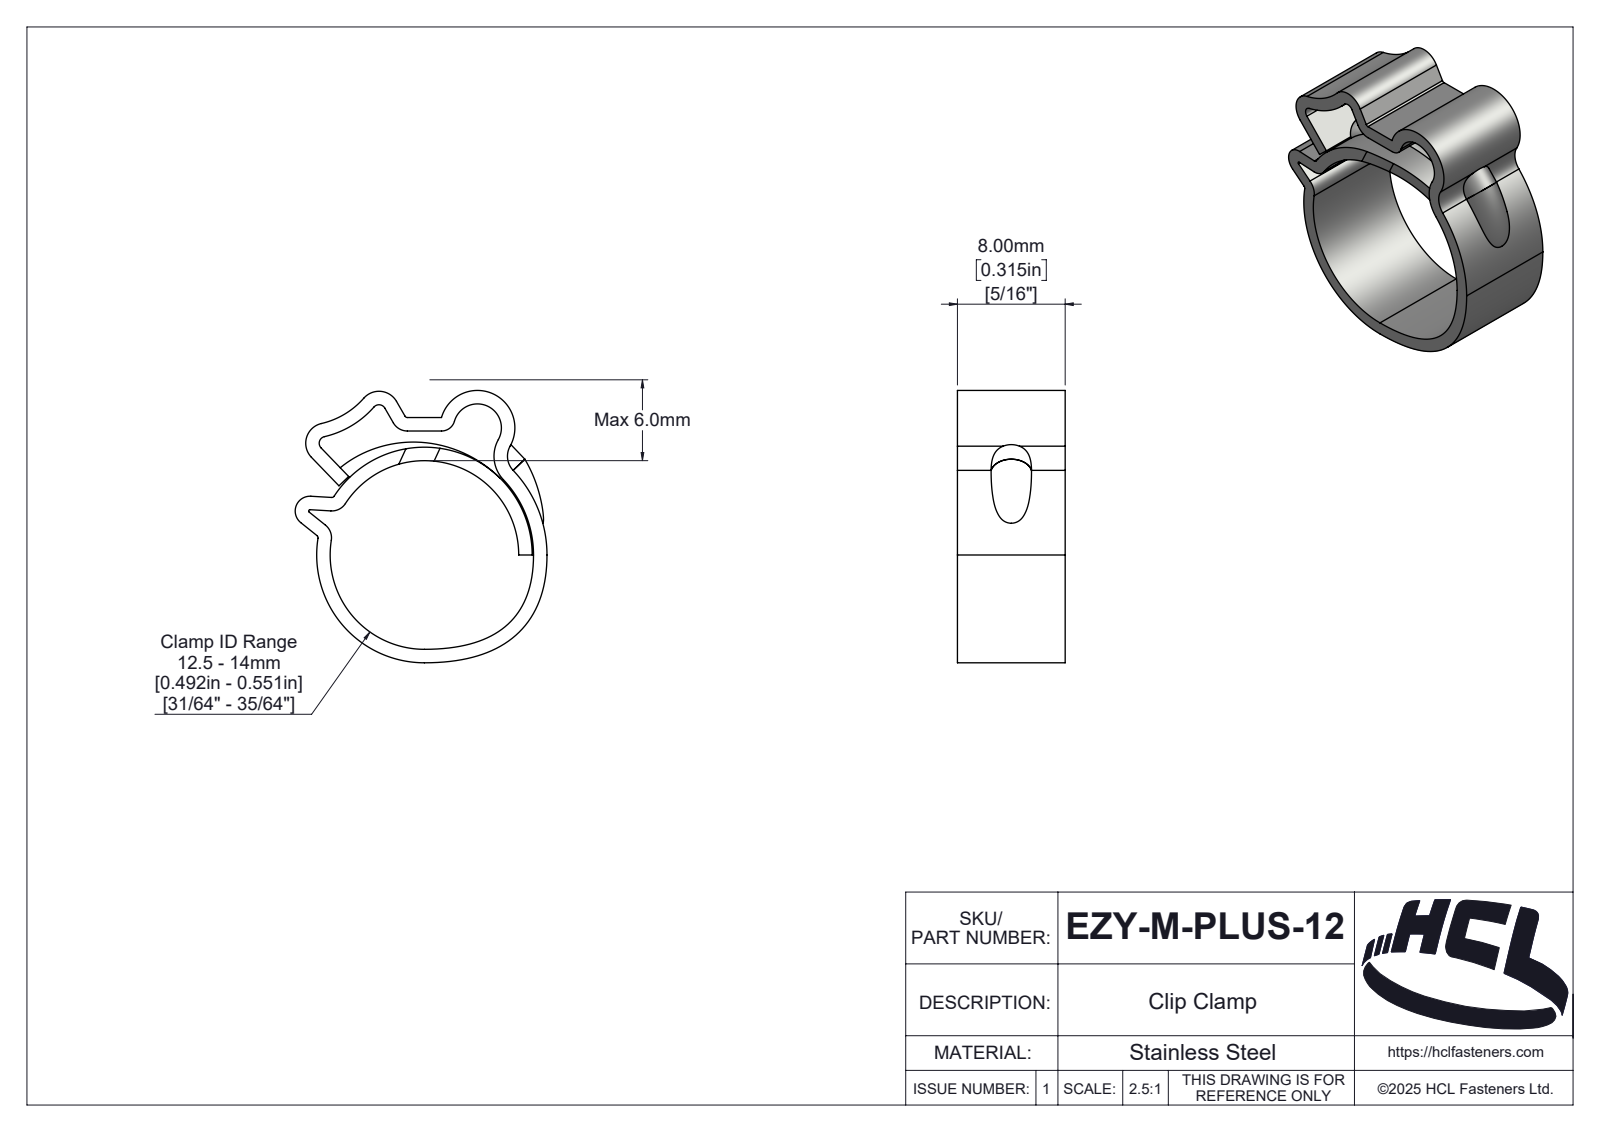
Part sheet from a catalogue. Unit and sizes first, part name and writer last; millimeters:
Units: millimetres
Overall size (bounding box): 20.21 × 18.7 × 8
Partial cylindrical surfaces — rounded edges, fillets, slot ends (radius × count): R0.2 ×3, R1.2 ×3, R0.5 ×2, R1.5 ×2, R7 ×2, R10 ×2, R0.1 ×1, R0.23 ×1
Main face-to-face distances: 1, 8, 9.2, 10.2
Volume: 661 mm³ · Surface area: 1 504 mm²
Bodies: 2 solids, 171 faces (21 planar, 86 cylindrical, 64 other)
Part name (STEP PRODUCT): EZY-M-PLUS-12
STEP written by: SolidWorks 2025 (AUTOMOTIVE_DESIGN)
